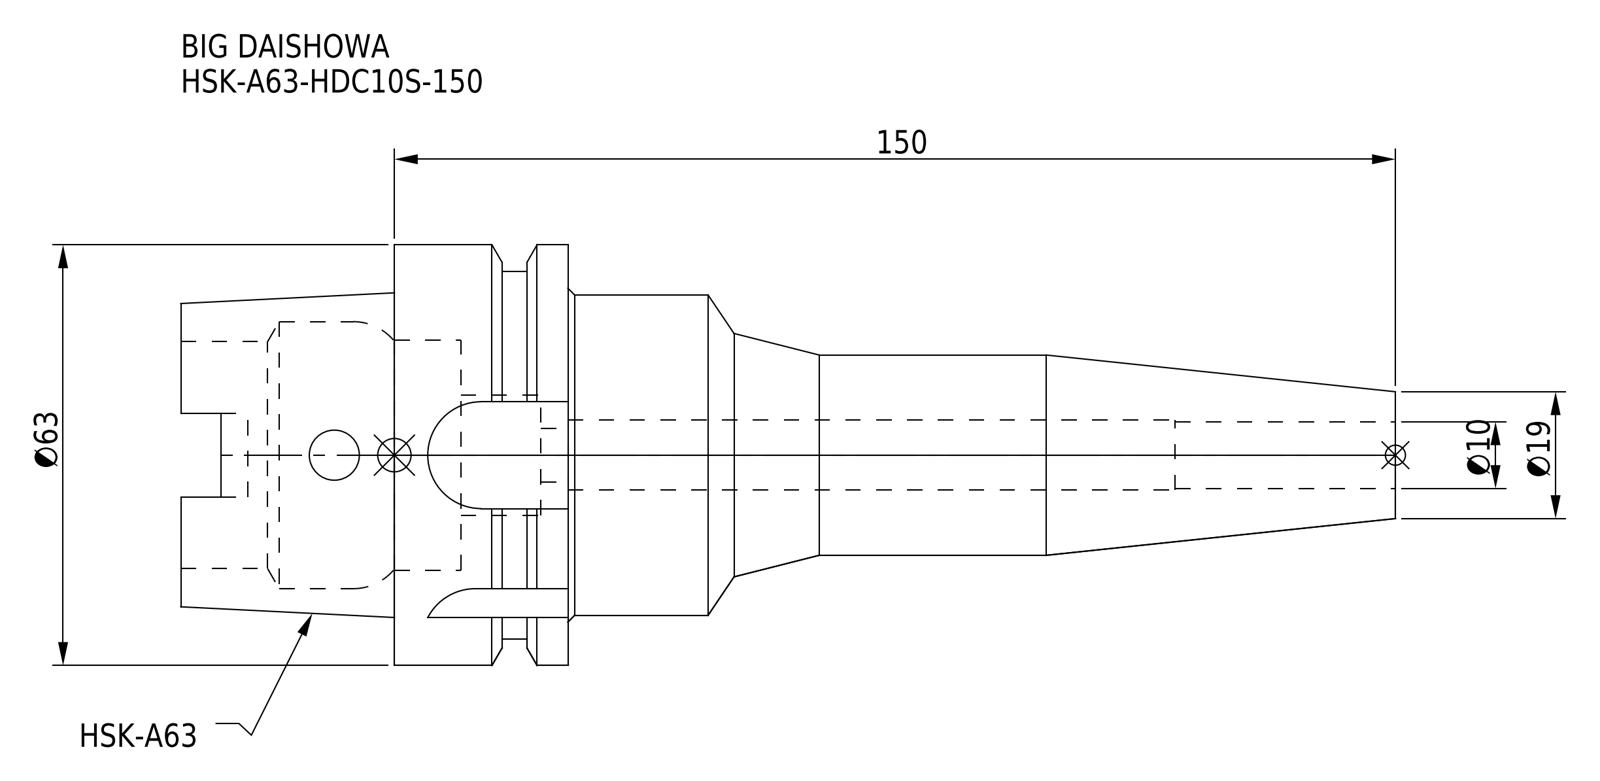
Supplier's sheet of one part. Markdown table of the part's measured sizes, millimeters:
| quantity | value |
| --- | --- |
| part name | HSK-A63-HDC10S-150 |
| STEP written by | CREO PARAMETRIC BY PTC INC, 2016380 (AUTOMOTIVE_DESIGN) |
| units | millimeters |
| bodies | 1 solid, 99 faces (38 planar, 39 cylindrical, 22 other) |
| overall size | 182 × 63 × 63 |
| volume | 174 944 mm³ |
| surface area | 37 479 mm² |
| round holes (diameter × count) | 7.5 × 1, 8 × 1, 10 × 1, 10.5 × 1, 18 × 1, 34 × 1, 34.5 × 1, 40 × 1 |
| round bosses / shafts (diameter × count) | 63 × 1, 55 × 1, 48 × 1, 30 × 1 |
| partial cylindrical surfaces (radius × count) | 2.88 × 4, 8 × 4 |
| main face-to-face distances | 26, 16.05, 9.95, 58, 41.95, 32, 53, 12, 124, 140.05 |
